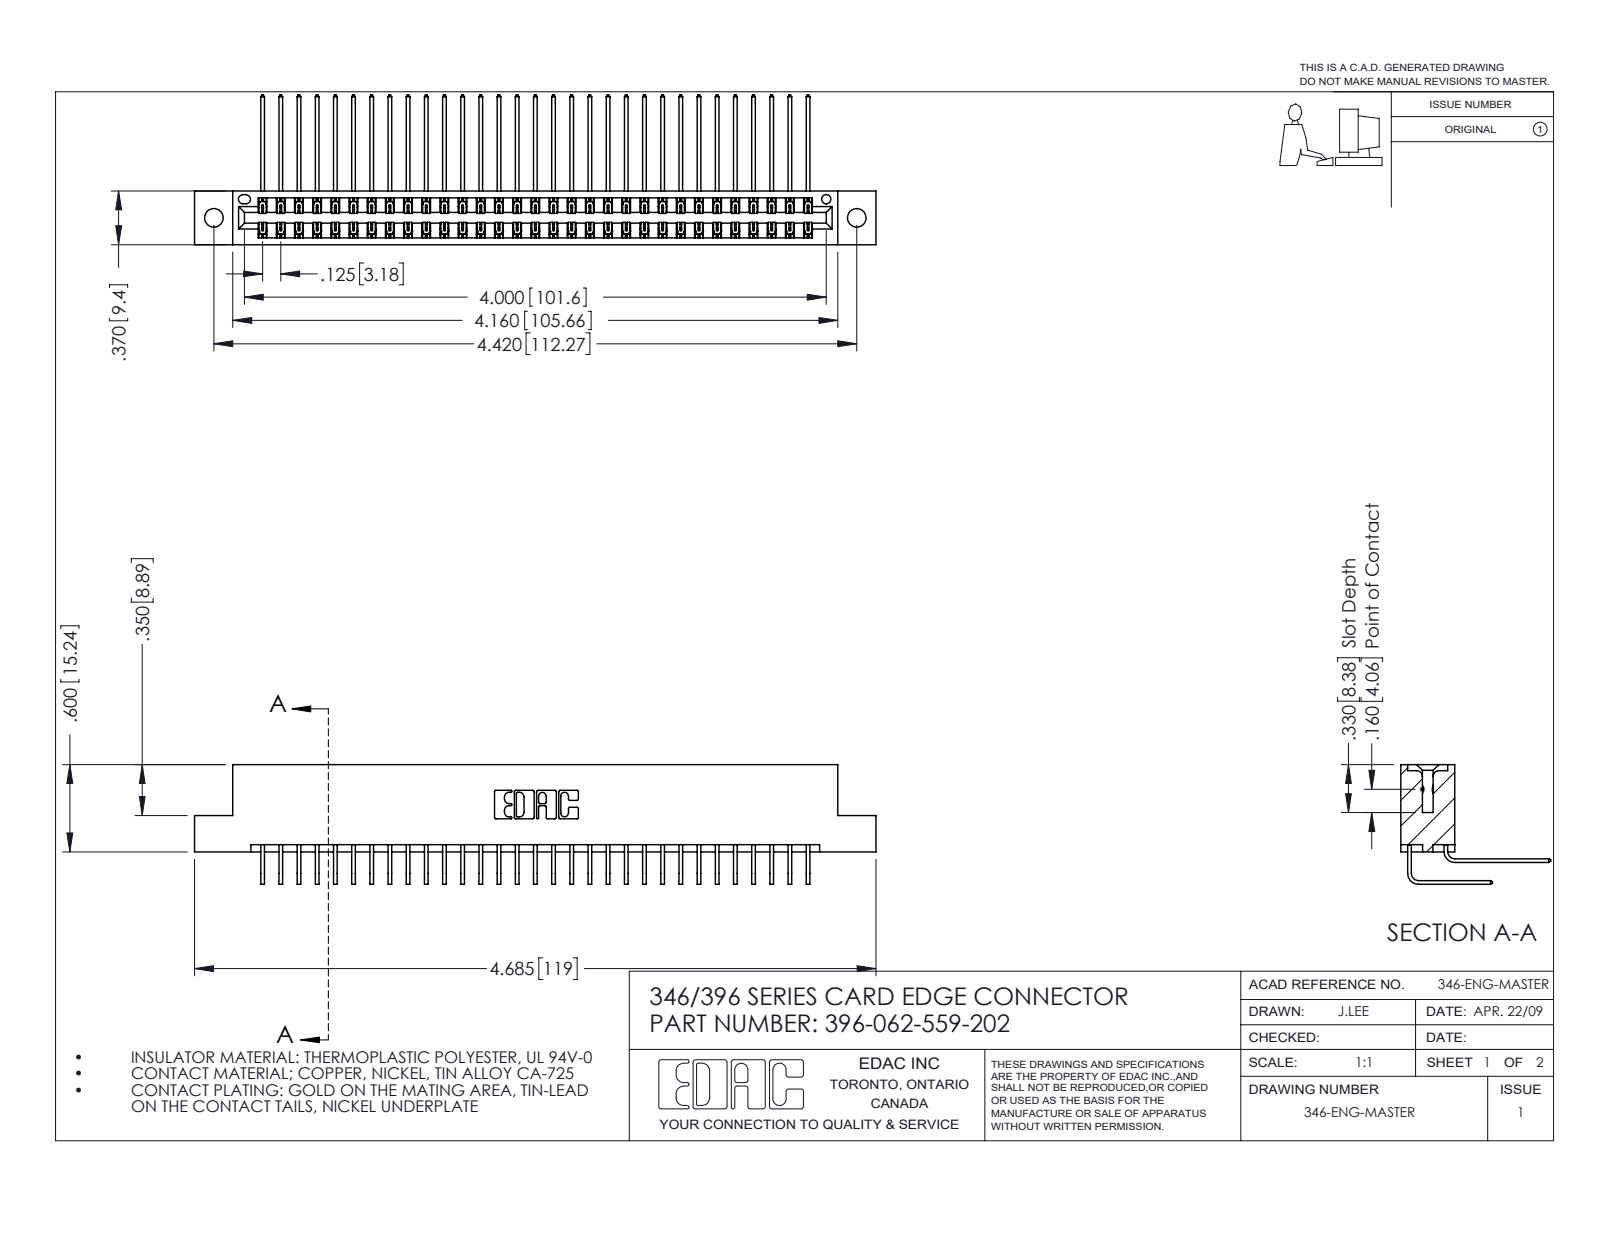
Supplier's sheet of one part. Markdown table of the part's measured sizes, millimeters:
| quantity | value |
| --- | --- |
| part name | 396-062-559-202; 346 Part_Flush Mounting Lugs - 0.128 Dia; 345-292-001_558 559 Tail - 1; 345-292-001_559 Tail - 2 |
| STEP written by | SolidWorks 2016 (CONFIG_CONTROL_DESIGN) |
| units | millimeters |
| bodies | 63 solids, 3470 faces (2370 planar, 1100 cylindrical, 0 other) |
| overall size | 119 × 26.2 × 20.9 |
| volume | 11 800 mm³ |
| surface area | 17 550 mm² |
| round holes (diameter × count) | 3.3 × 2, 1.6 × 1 |
| partial cylindrical surfaces (radius × count) | 0.2 × 93, 0.3 × 22, 0.2 × 6, 0.8 × 6, 0.7 × 3, 0.4 × 2, 0.6 × 2, 0.6 × 2 |
| main face-to-face distances | 1.2, 8.2, 0.6, 6.4, 9.4, 1.8, 7.6, 7, 3.8, 5.6 |
| hole center spacings | 6.2, 107, 112.3 |
